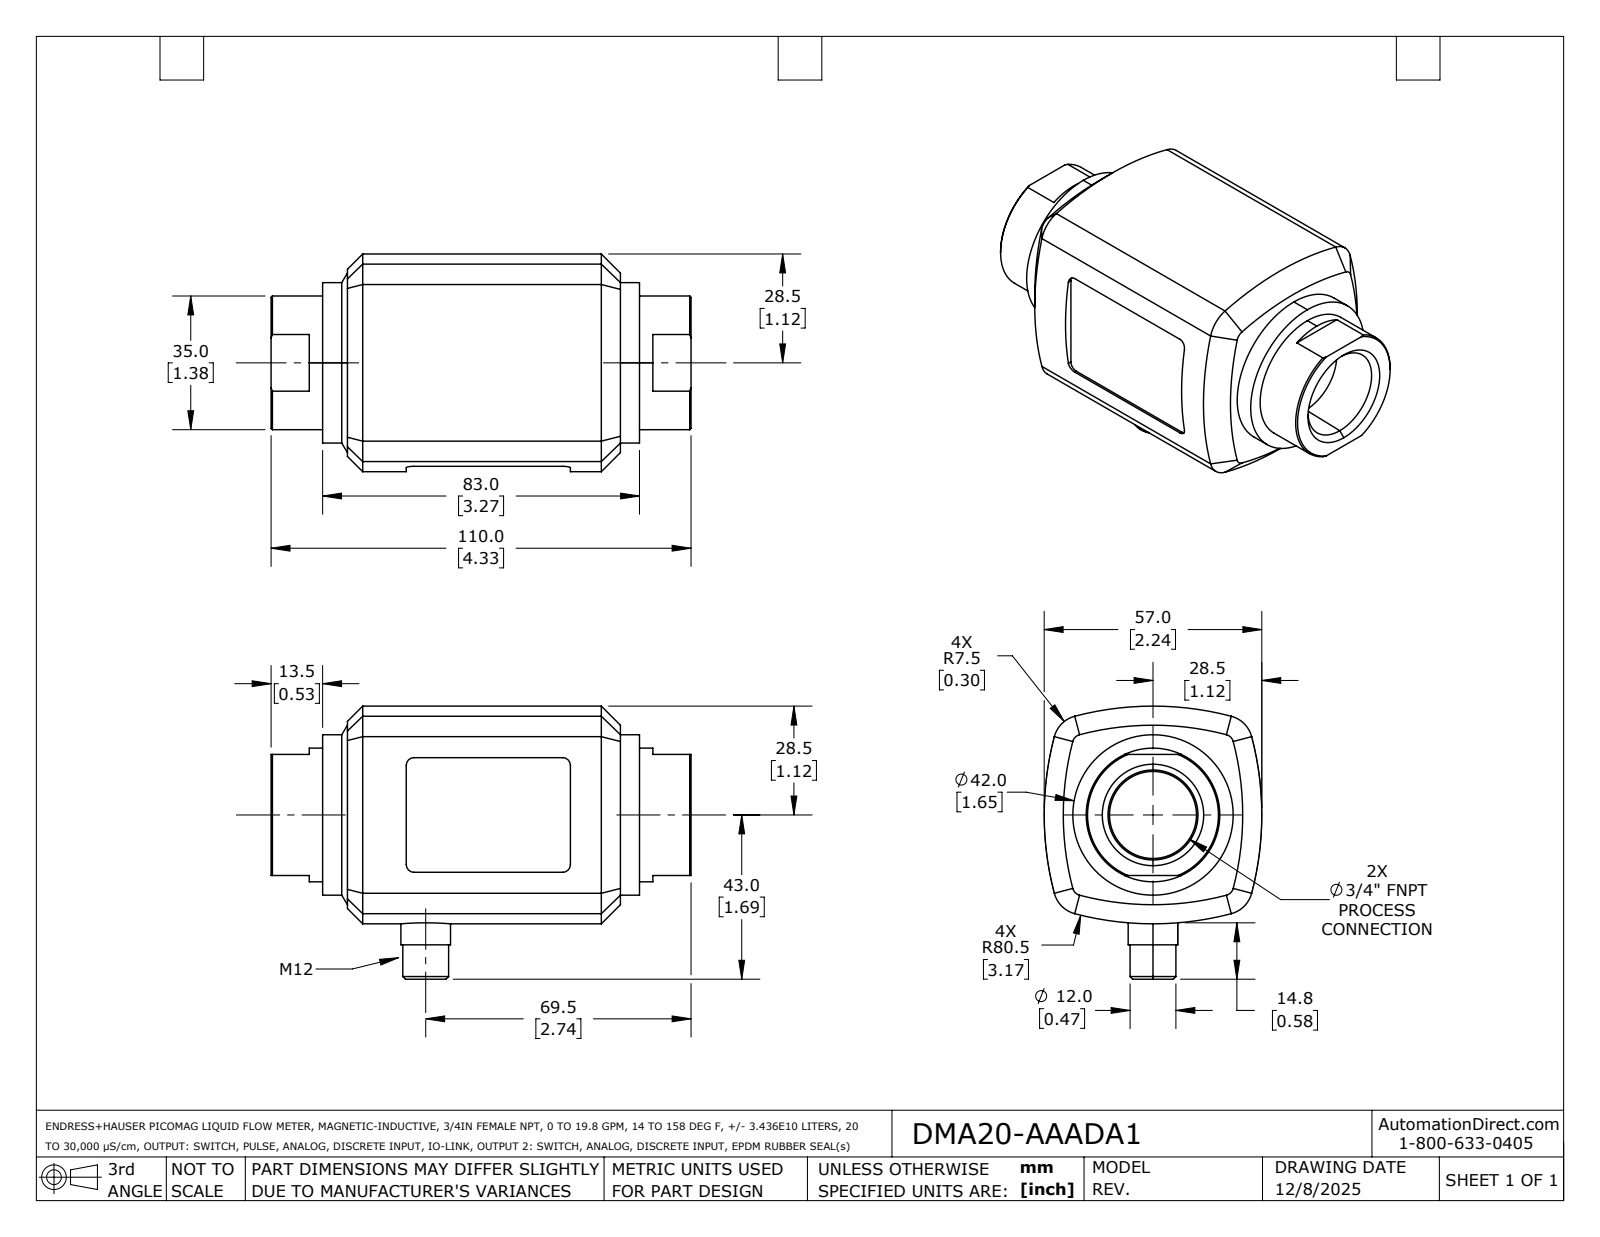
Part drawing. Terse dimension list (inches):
name: DMA20-AAADA1
written by: SolidWorks 2024 (AUTOMOTIVE_DESIGN)
unit: in
bodies: 1 solid, 82 faces (24 planar, 26 cylindrical, 32 other)
size: 4.331 × 2.815 × 2.244
volume: 14.28 in³; area: 40.27 in²
holes: 1× ⌀0.382
bosses: 1× ⌀1.654, 1× ⌀1.378, 1× ⌀0.512, 1× ⌀0.472
rounds: 4× R0.079, 4× R0.295, 4× R3.169
face distances: 0.022, 3.246, 0.531, 0.553, 3.778, 3.799, 2.815, 0.256, 3.071, 3.268
